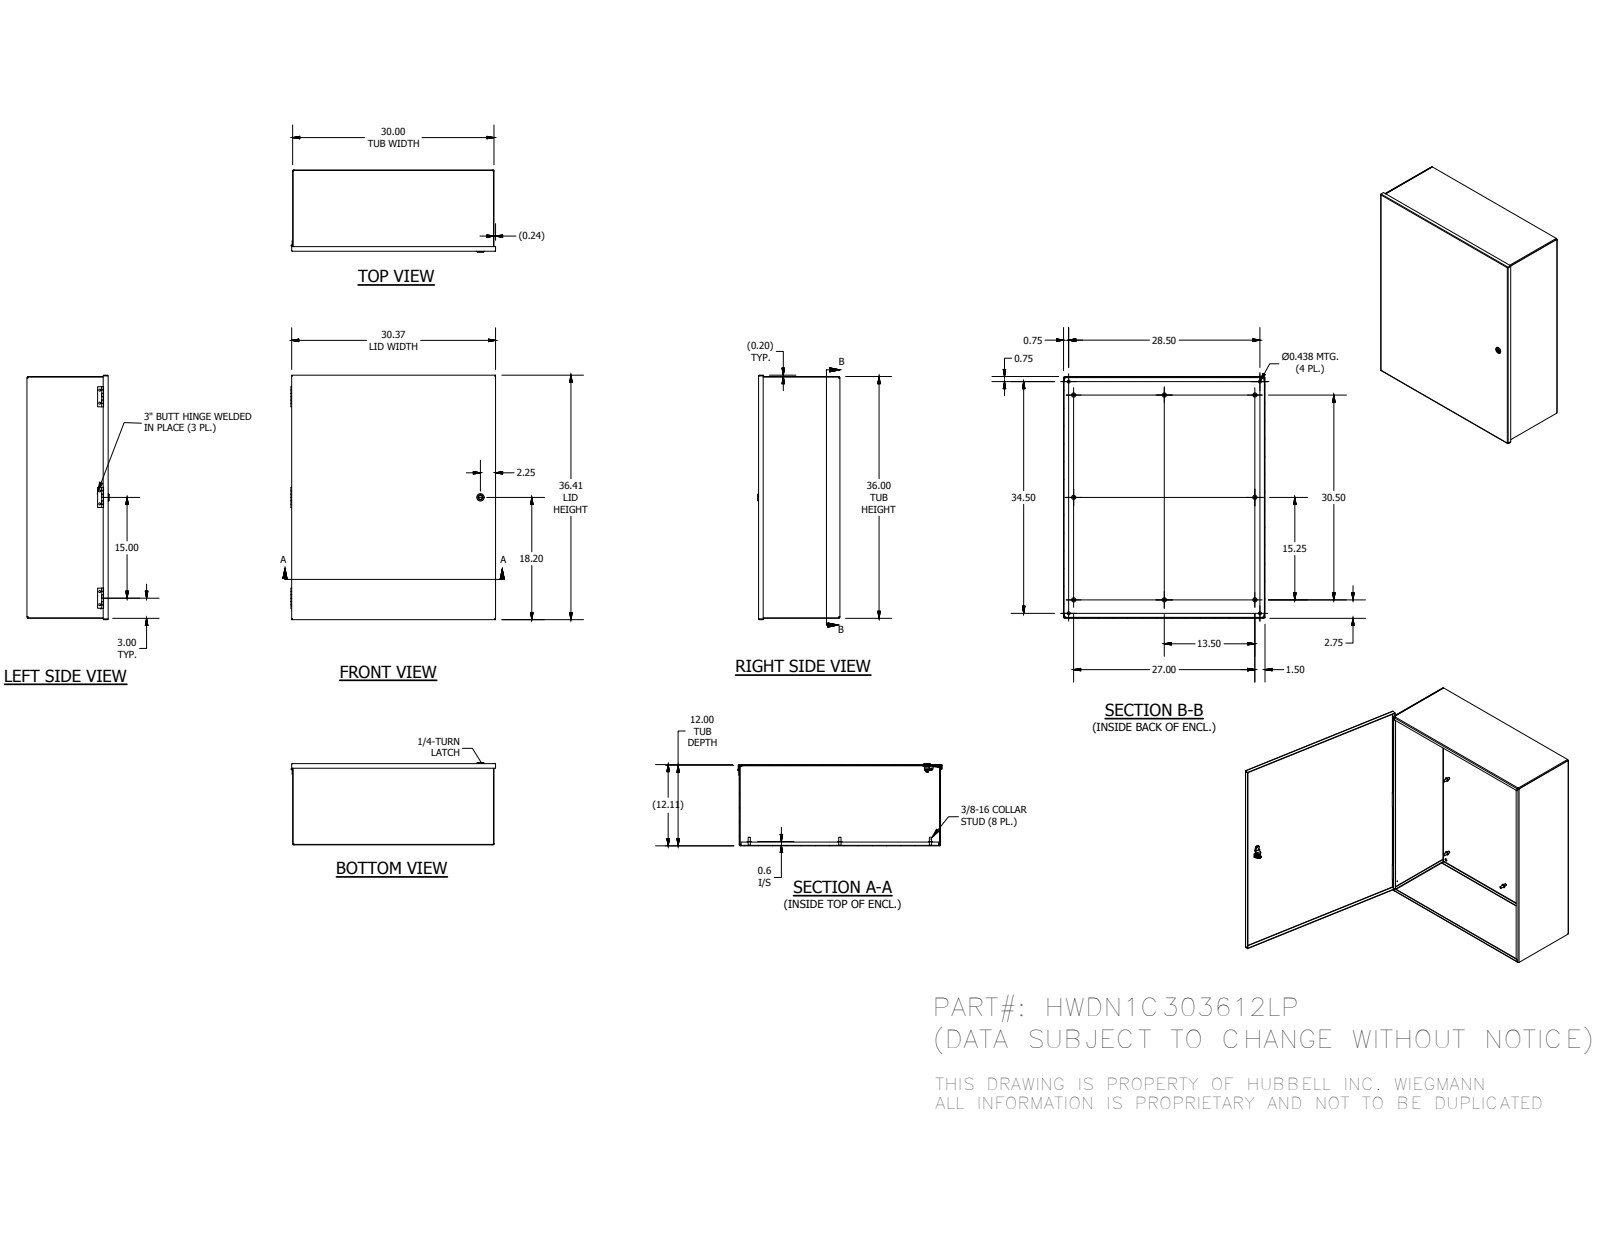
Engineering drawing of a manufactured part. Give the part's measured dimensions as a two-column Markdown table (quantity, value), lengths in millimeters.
| quantity | value |
| --- | --- |
| part name | N1C303612LPBLR; N1C3012LPTB; N1C3036LPLID; 1000-101-GPF_GPD (+8 more) |
| STEP written by | Autodesk Inventor 2016 (AUTOMOTIVE_DESIGN) |
| units | millimeters |
| bodies | 28 solids, 796 faces (484 planar, 239 cylindrical, 73 other) |
| overall size | 924.72 × 774.41 × 330.52 |
| volume | 4 932 000 mm³ |
| surface area | 5 268 000 mm² |
| round holes (diameter × count) | 7.95 × 6, 11.11 × 4, 3.05 × 1, 3.3 × 1, 5 × 1, 8 × 1, 10 × 1, 10.2 × 1, 16.1 × 1, 20.38 × 1 |
| round bosses / shafts (diameter × count) | 15.88 × 8, 8.38 × 8, 28 × 1, 27 × 1, 23 × 1, 19.8 × 1, 15.8 × 1, 15.2 × 1 |
| partial cylindrical surfaces (radius × count) | 0.3 × 30, 1.59 × 12, 3.47 × 12, 0.5 × 10, 0.79 × 4, 2.67 × 4, 4 × 4, 0.4 × 3 |
| main face-to-face distances | 1.88, 324.64, 322.76, 326.52, 760.12, 912.52, 758.24, 762, 910.64, 914.4 |
| hole center spacings | 381, 49.28, 331.72, 430.28, 439.32, 723.9, 762, 818.93 |
